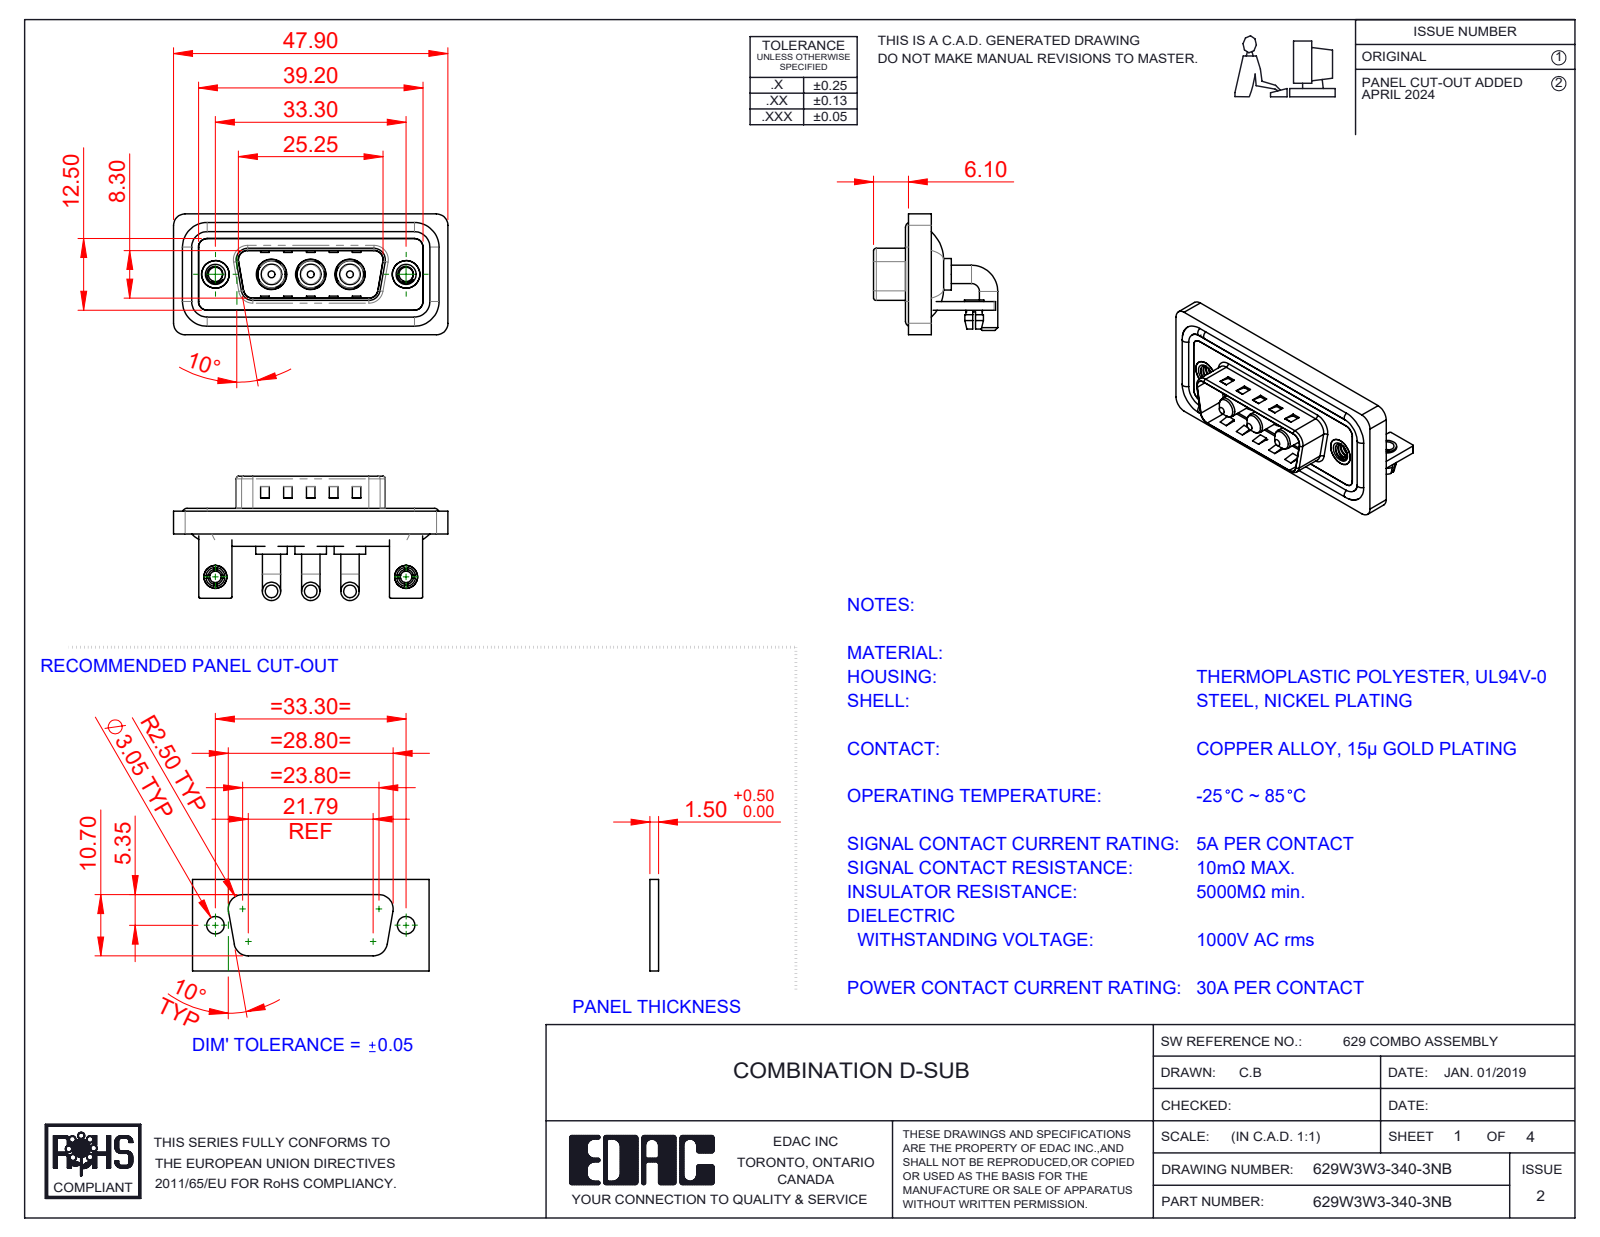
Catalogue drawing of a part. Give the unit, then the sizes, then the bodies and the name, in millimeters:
Units: millimetres
Overall size (bounding box): 47.9 × 21.7 × 21.1
Round holes (diameter × count): ⌀2.5 ×4, ⌀4.85 ×3, ⌀5.3 ×3, ⌀2 ×2, ⌀3.2 ×2, ⌀4 ×2, ⌀4.8 ×2, ⌀5 ×2
Round bosses / shafts (diameter × count): ⌀3.2 ×6, ⌀1.6 ×4, ⌀5.5 ×3, ⌀5.2 ×3, ⌀4.75 ×3, ⌀3.75 ×3, ⌀3.6 ×3, ⌀4.9 ×2
Partial cylindrical surfaces — rounded edges, fillets, slot ends (radius × count): R2 ×21, R1.5 ×18, R0.25 ×16, R0.5 ×9, R1.6 ×8, R0.6 ×4, R0.65 ×4, R0.9 ×4
Main face-to-face distances: 0.4, 1.5, 0.8, 2.9, 1.1, 2.1, 3.7, 1.6, 1.2, 4.5
Hole centre spacings: 6.85, 9.8, 16.65, 23.5, 33.3, 13.7
Volume: 6 171 mm³ · Surface area: 9 890 mm²
Bodies: 17 solids, 706 faces (275 planar, 297 cylindrical, 134 other)
Part name (STEP PRODUCT): 629Combo Shell Rear_15 Contacts; 629Combo Housing_3W3; 629Combo Stabilizer Bracket; 629W3W3-340-3NB (+5 more)
STEP written by: SolidWorks 2023 (CONFIG_CONTROL_DESIGN)
